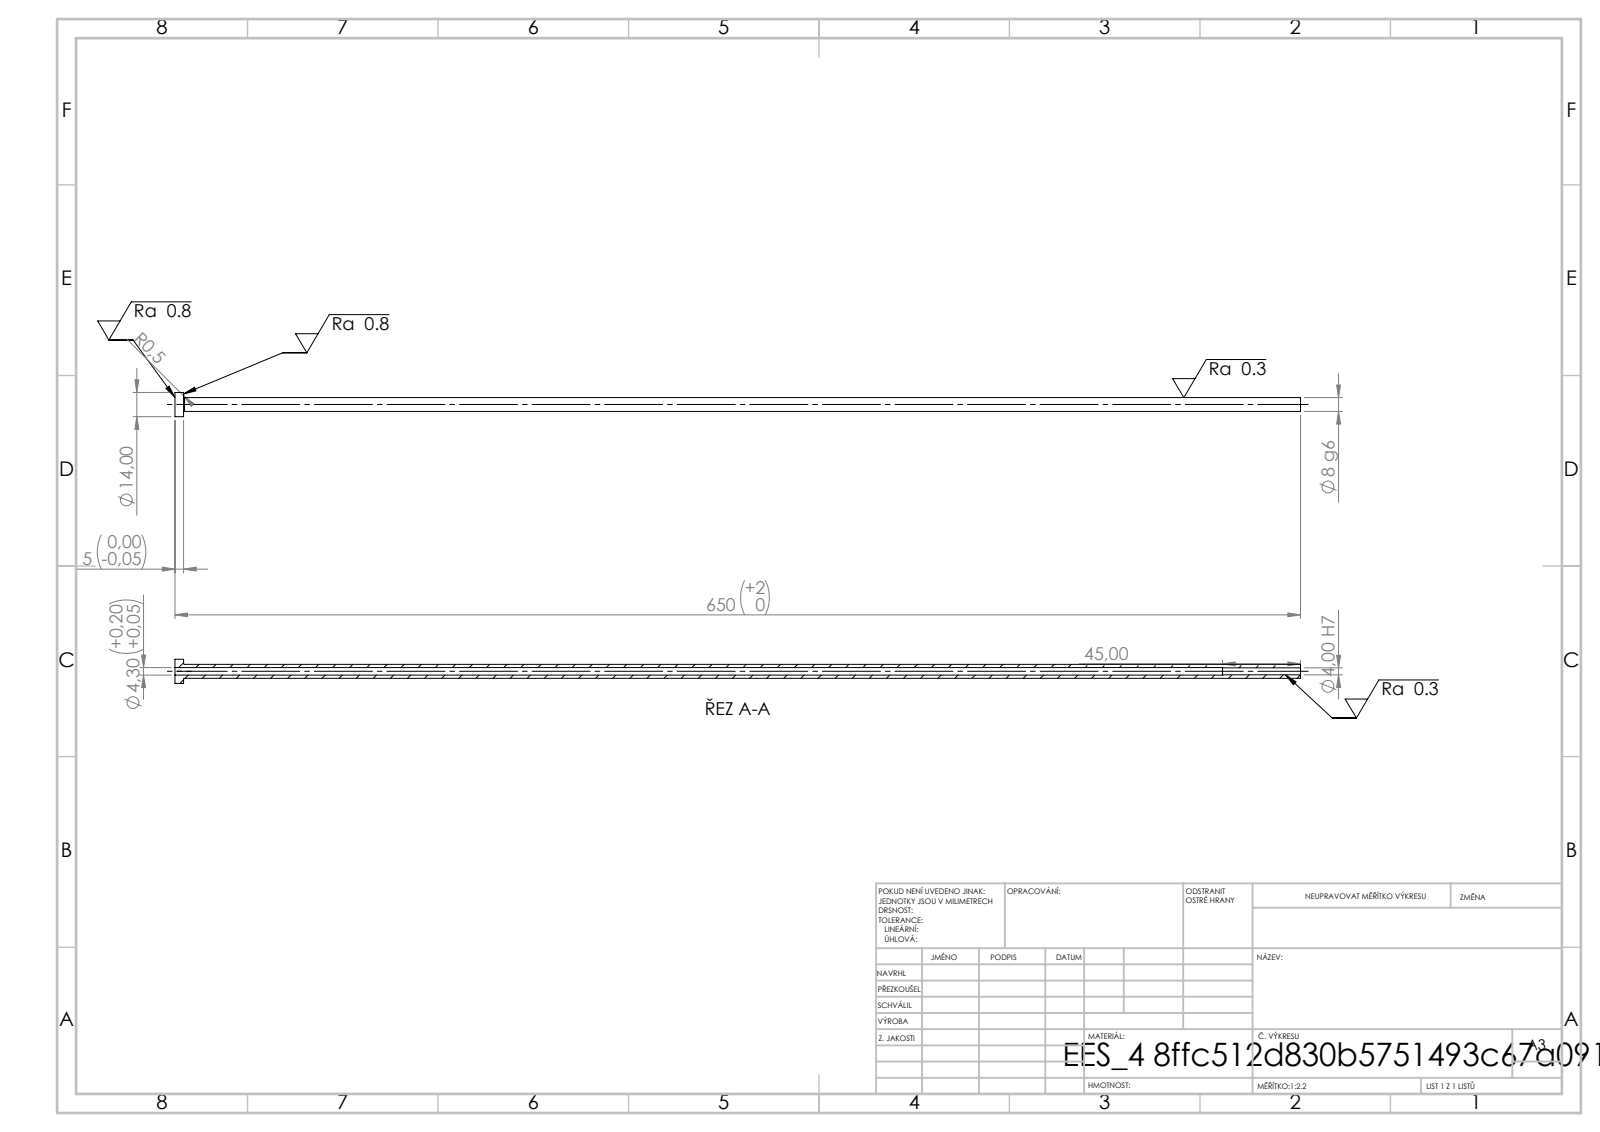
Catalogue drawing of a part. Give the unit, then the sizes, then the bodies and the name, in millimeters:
Units: millimetres
Overall size (bounding box): 650 × 14 × 14
Round holes (diameter × count): ⌀4 ×1, ⌀4.3 ×1
Round bosses / shafts (diameter × count): ⌀14 ×1, ⌀8 ×1
Main face-to-face distances: 5, 650, 645, 605, 600, 45
Volume: 23 841 mm³ · Surface area: 25 446 mm²
Bodies: 1 solid, 14 faces (4 planar, 8 cylindrical, 2 other)
STEP written by: SolidWorks 2019 (CONFIG_CONTROL_DESIGN)
